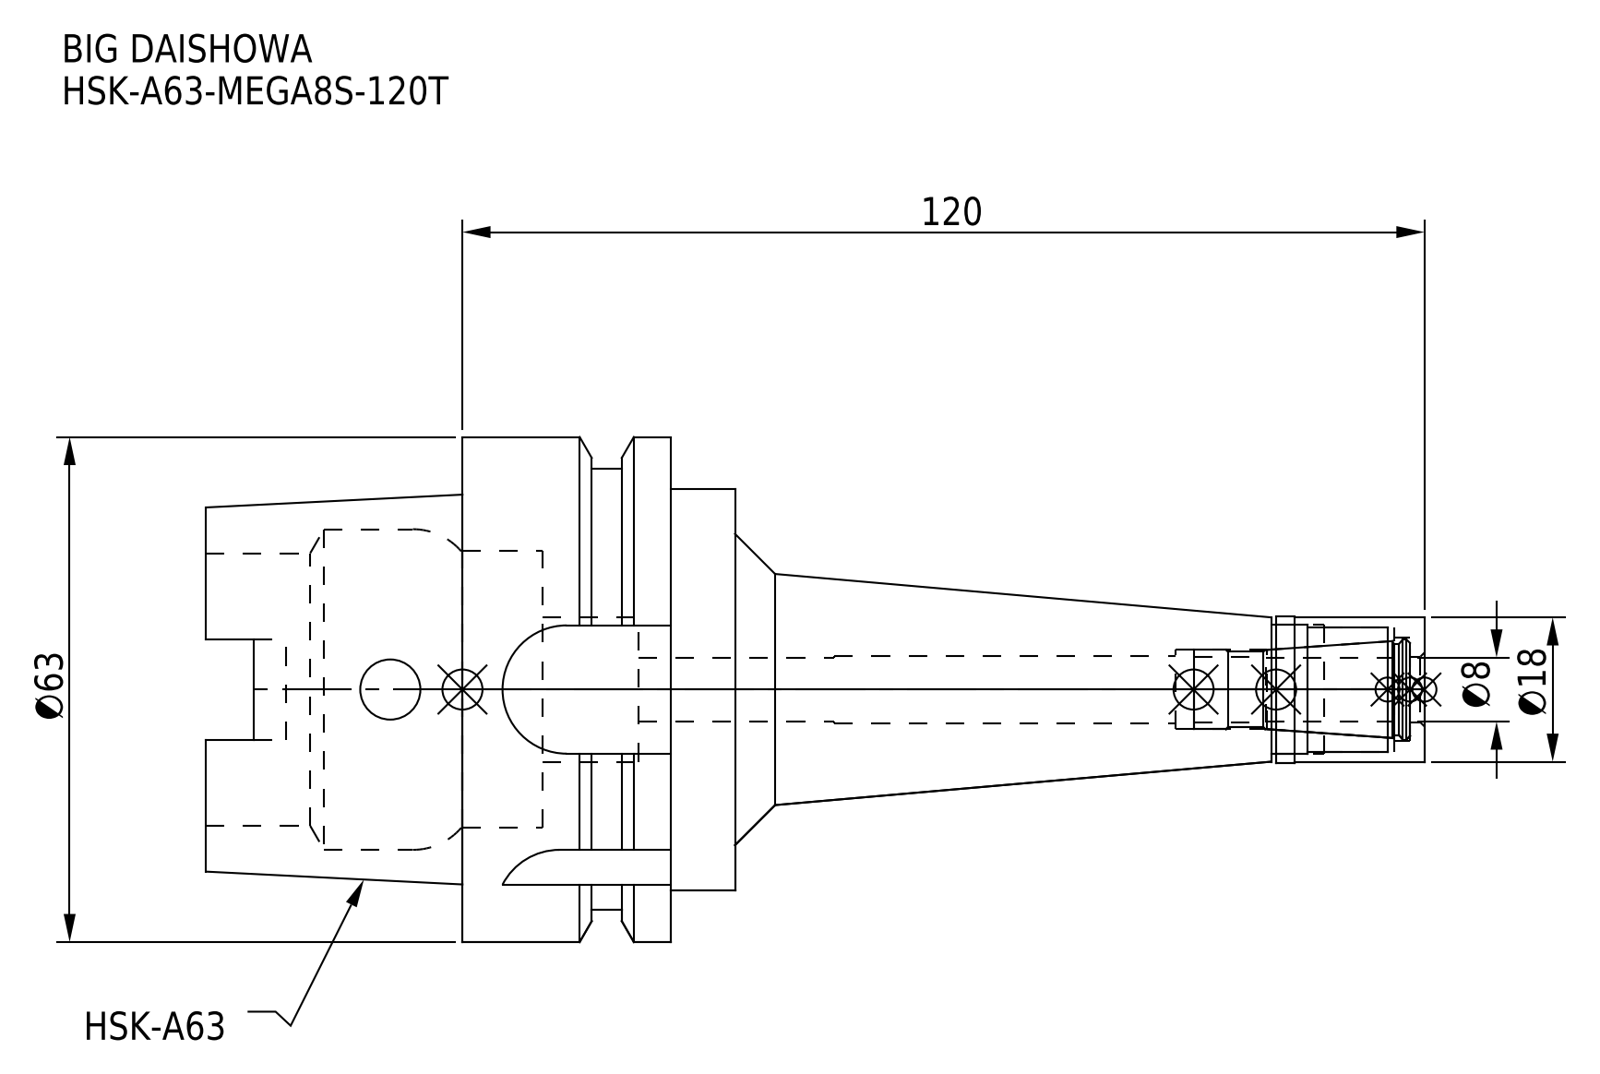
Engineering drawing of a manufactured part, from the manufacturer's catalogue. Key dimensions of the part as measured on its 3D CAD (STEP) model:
Part name (STEP PRODUCT): DXF_TEMP_ASSY_ASM_4_ASM.stp; MGN8S_1.stp; HSK-A63-MEGA8S-120T-080-FreeParts; HA63MS08120T-080_ASM.stp (+3 more)
STEP written by: SolidWorks 2019 (CONFIG_CONTROL_DESIGN)
Units: millimetres
Bodies: 2 solids, 122 faces (47 planar, 53 cylindrical, 22 other)
Overall size (bounding box): 152 × 63 × 63
Volume: 127 653 mm³ · Surface area: 33 479 mm²
Round holes (diameter × count): ⌀7.5 ×1, ⌀8 ×1, ⌀8.2 ×1, ⌀8.4 ×1, ⌀9.9 ×1, ⌀12.9 ×1, ⌀15.6 ×1, ⌀16.1 ×1, ⌀18 ×1, ⌀34 ×1, ⌀34.5 ×1, ⌀40 ×1
Round bosses / shafts (diameter × count): ⌀63 ×1, ⌀55 ×1, ⌀50 ×1, ⌀18.3 ×1
Partial cylindrical surfaces — rounded edges, fillets, slot ends (radius × count): R2.88 ×4, R8 ×4
Main face-to-face distances: 26, 8, 34, 24.05, 16.05, 9.95, 66, 58, 41.95, 32
